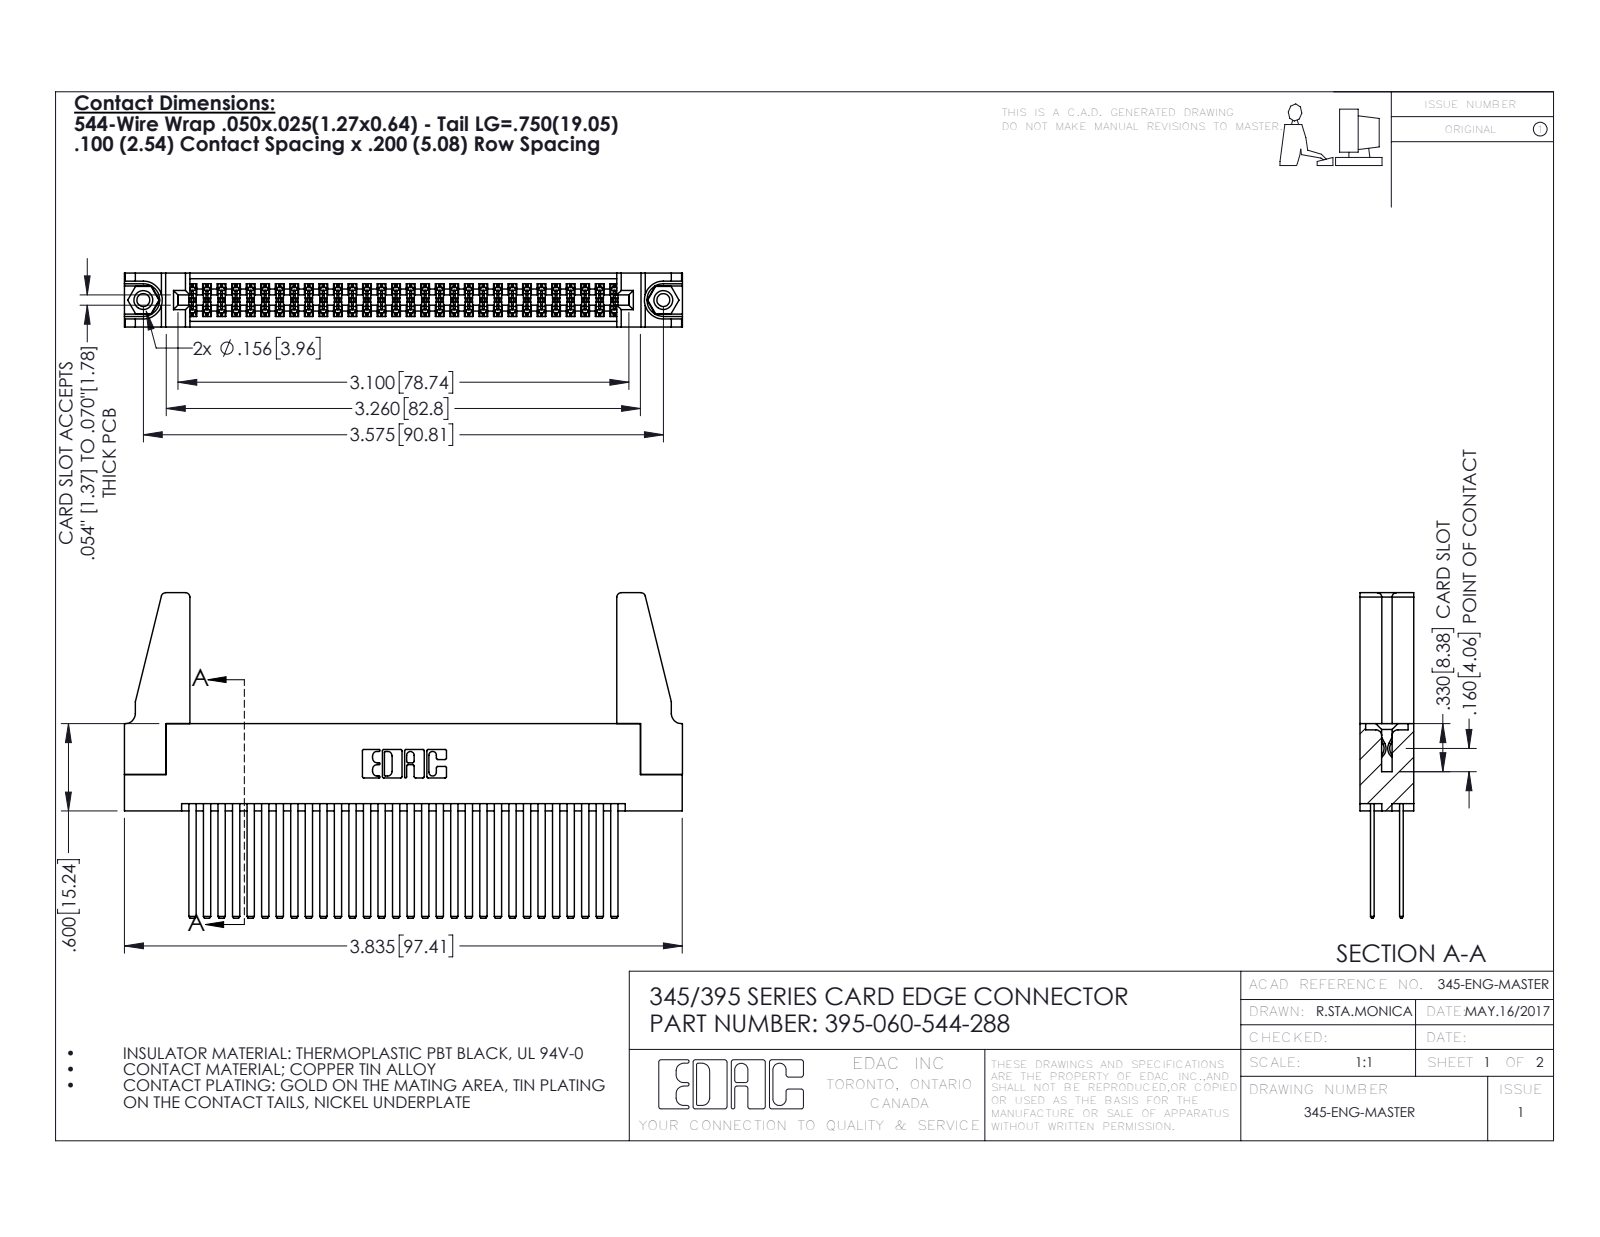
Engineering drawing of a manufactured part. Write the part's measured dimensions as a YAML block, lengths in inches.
part_name: "345-292-001_345-293-144; 395-060-544-288; 345 Part_Flush Mounting Lugs - 0.156 Dia-TH; 345-220-078_345-220-088 (+1 more)"
step_written_by: "SolidWorks 2016 (CONFIG_CONTROL_DESIGN)"
units: inches
bodies: {solids: 65, faces: 2890, planar: 1892, cylindrical: 982, other: 16}
overall_size: [3.836, 2.237, 0.37]
volume: 0.821
surface_area: 31.66
round_holes:
  - {diameter: 0.089, count: 2}
  - {diameter: 0.125, count: 2}
  - {diameter: 0.156, count: 2}
  - {diameter: 0.064, count: 1}
round_bosses_or_shafts:
  - {diameter: 0.155, count: 2}
partial_cylinders:
  - {radius: 0.006, count: 90}
  - {radius: 0.01, count: 22}
  - {radius: 0.03, count: 8}
  - {radius: 0.007, count: 6}
  - {radius: 0.031, count: 6}
  - {radius: 0.026, count: 3}
  - {radius: 0.014, count: 2}
  - {radius: 0.019, count: 2}
face_to_face_distances: [0.072, 0.298, 0.2, 0.098, 0.272, 0.025, 0.37, 0.225, 0.175, 0.05]
hole_center_spacings: [0.27, 3.34, 3.575]
